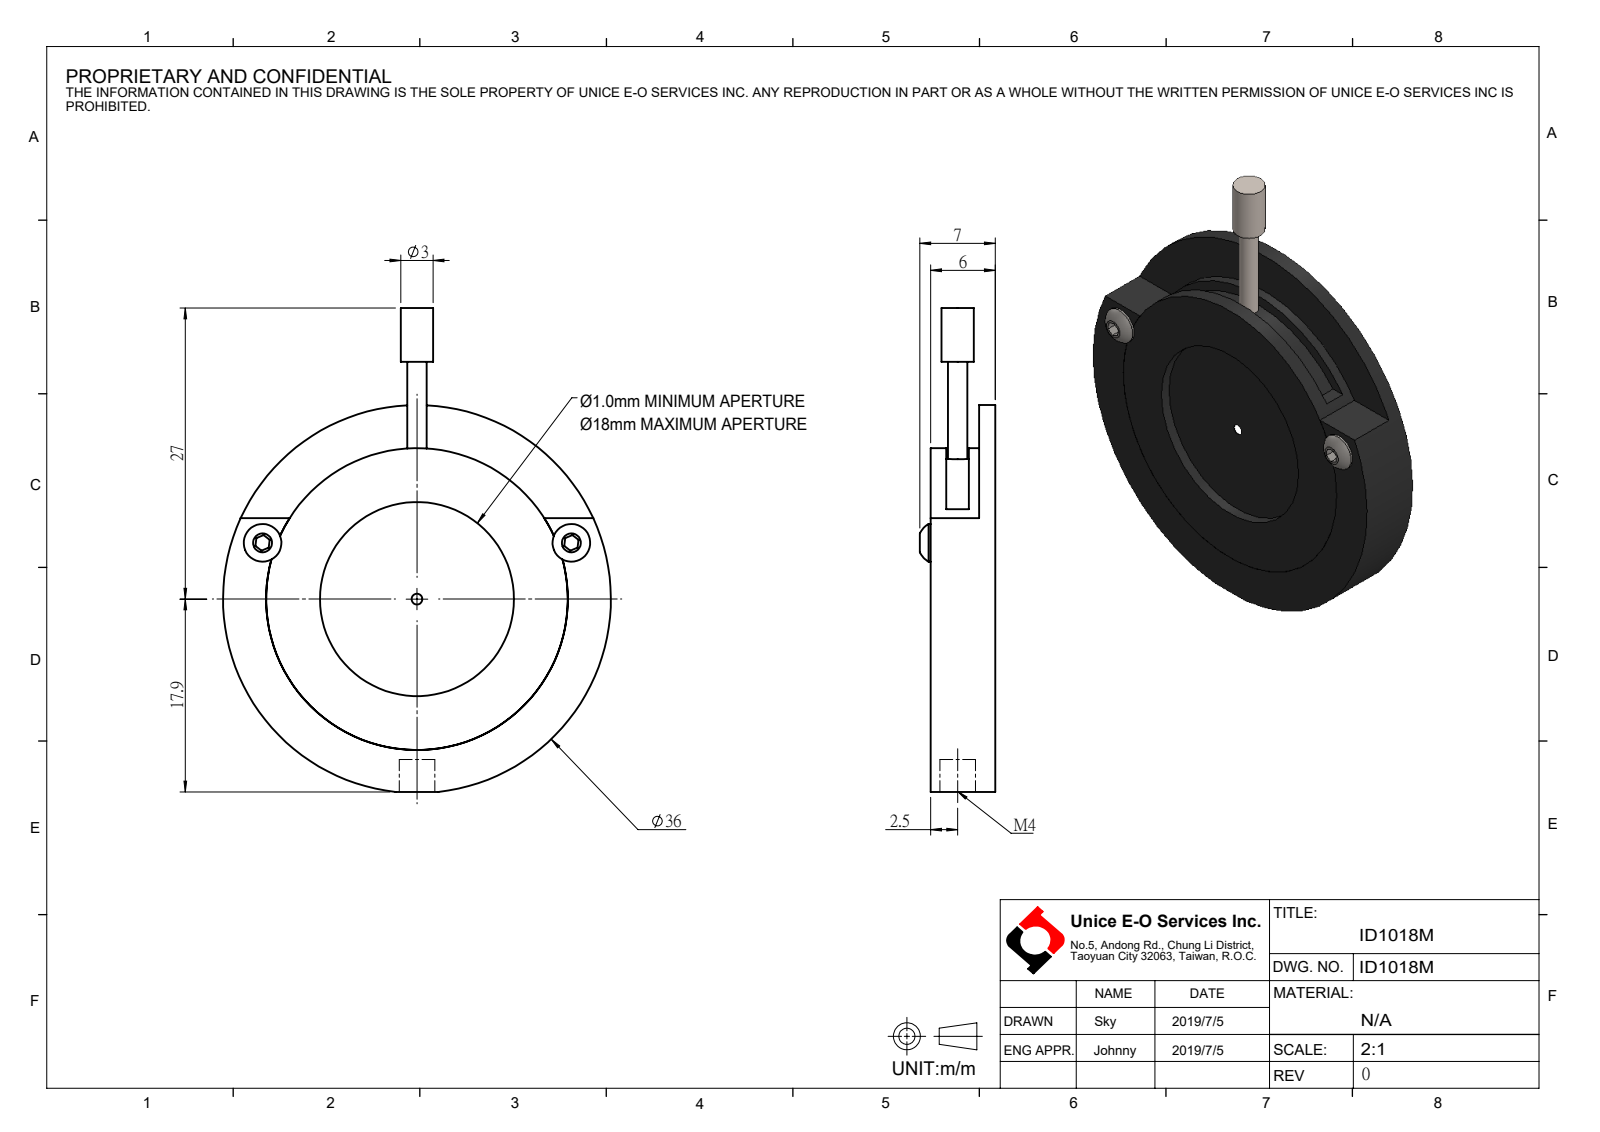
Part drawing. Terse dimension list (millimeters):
name: ID1018M
written by: SolidWorks 2016 (AUTOMOTIVE_DESIGN)
unit: mm
bodies: 0 solids, 62 faces (30 planar, 28 cylindrical, 4 other)
size: 44.89 × 36 × 7
holes: 1× ⌀1, 1× ⌀3.3, 1× ⌀18, 1× ⌀25, 1× ⌀26, 1× ⌀28
bosses: 2× ⌀3.5, 1× ⌀36, 1× ⌀3, 1× ⌀1.8
face distances: 6, 2, 4, 5, 1, 4.9, 2.9, 3, 1.1, 1.5
